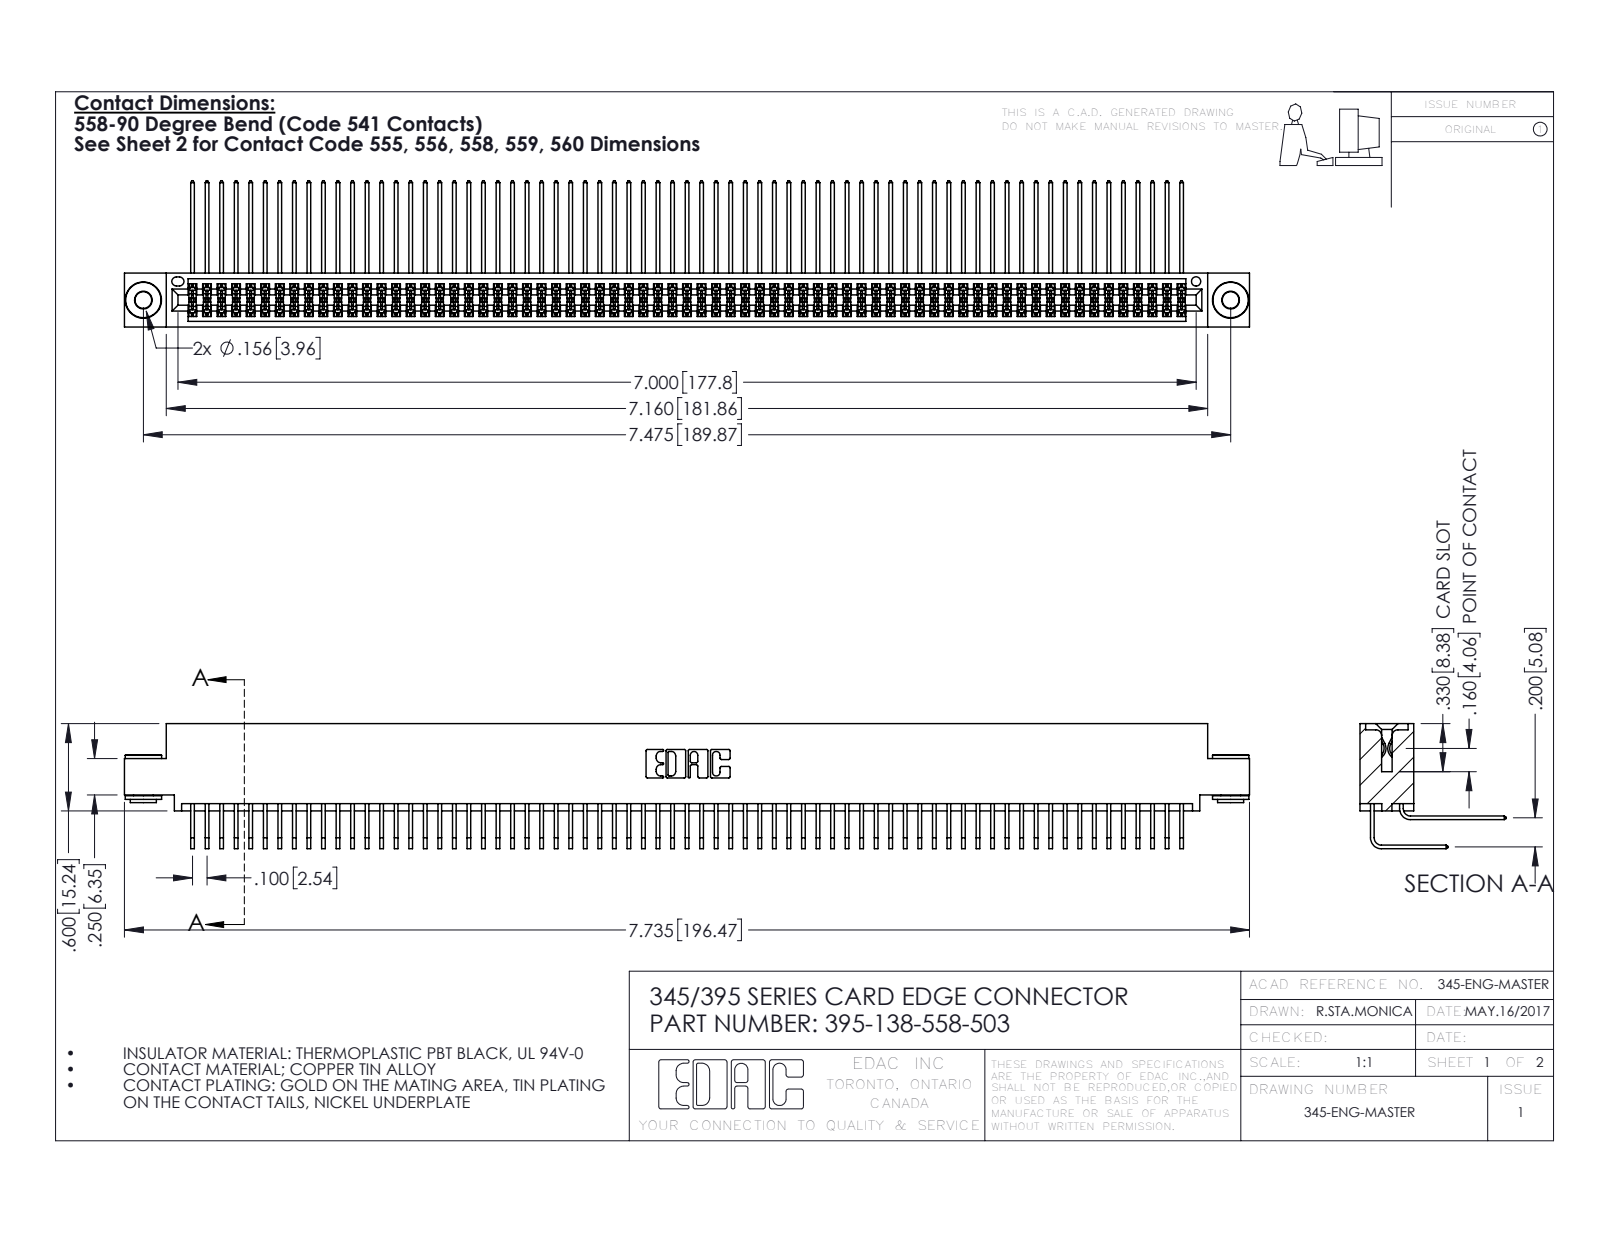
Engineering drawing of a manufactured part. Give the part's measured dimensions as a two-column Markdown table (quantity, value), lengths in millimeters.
| quantity | value |
| --- | --- |
| part name | 345 Part_0.110 Offset - 0.156 Dia-TH; 395-138-558-503; 345-250-002_345-250-002-102; 345-292-001_558 559 Tail - 1 (+1 more) |
| STEP written by | SolidWorks 2016 (CONFIG_CONTROL_DESIGN) |
| units | millimeters |
| bodies | 141 solids, 7344 faces (4924 planar, 2412 cylindrical, 8 other) |
| overall size | 196.5 × 25.5 × 21.8 |
| volume | 20 070 mm³ |
| surface area | 34 250 mm² |
| round holes (diameter × count) | 2.9 × 2, 4 × 2, 1.6 × 1 |
| round bosses / shafts (diameter × count) | 6.4 × 2, 4.6 × 2, 3.5 × 2 |
| partial cylindrical surfaces (radius × count) | 0.2 × 275, 0.3 × 22, 0.2 × 6, 0.8 × 6, 0.7 × 3, 0.4 × 2, 0.5 × 2, 0.6 × 2 |
| main face-to-face distances | 1.8, 7.6, 5.1, 0.6, 9.4, 2.5, 6.9, 5.7, 0.6, 4.4 |
| hole center spacings | 6.9, 183.9, 189.9 |
